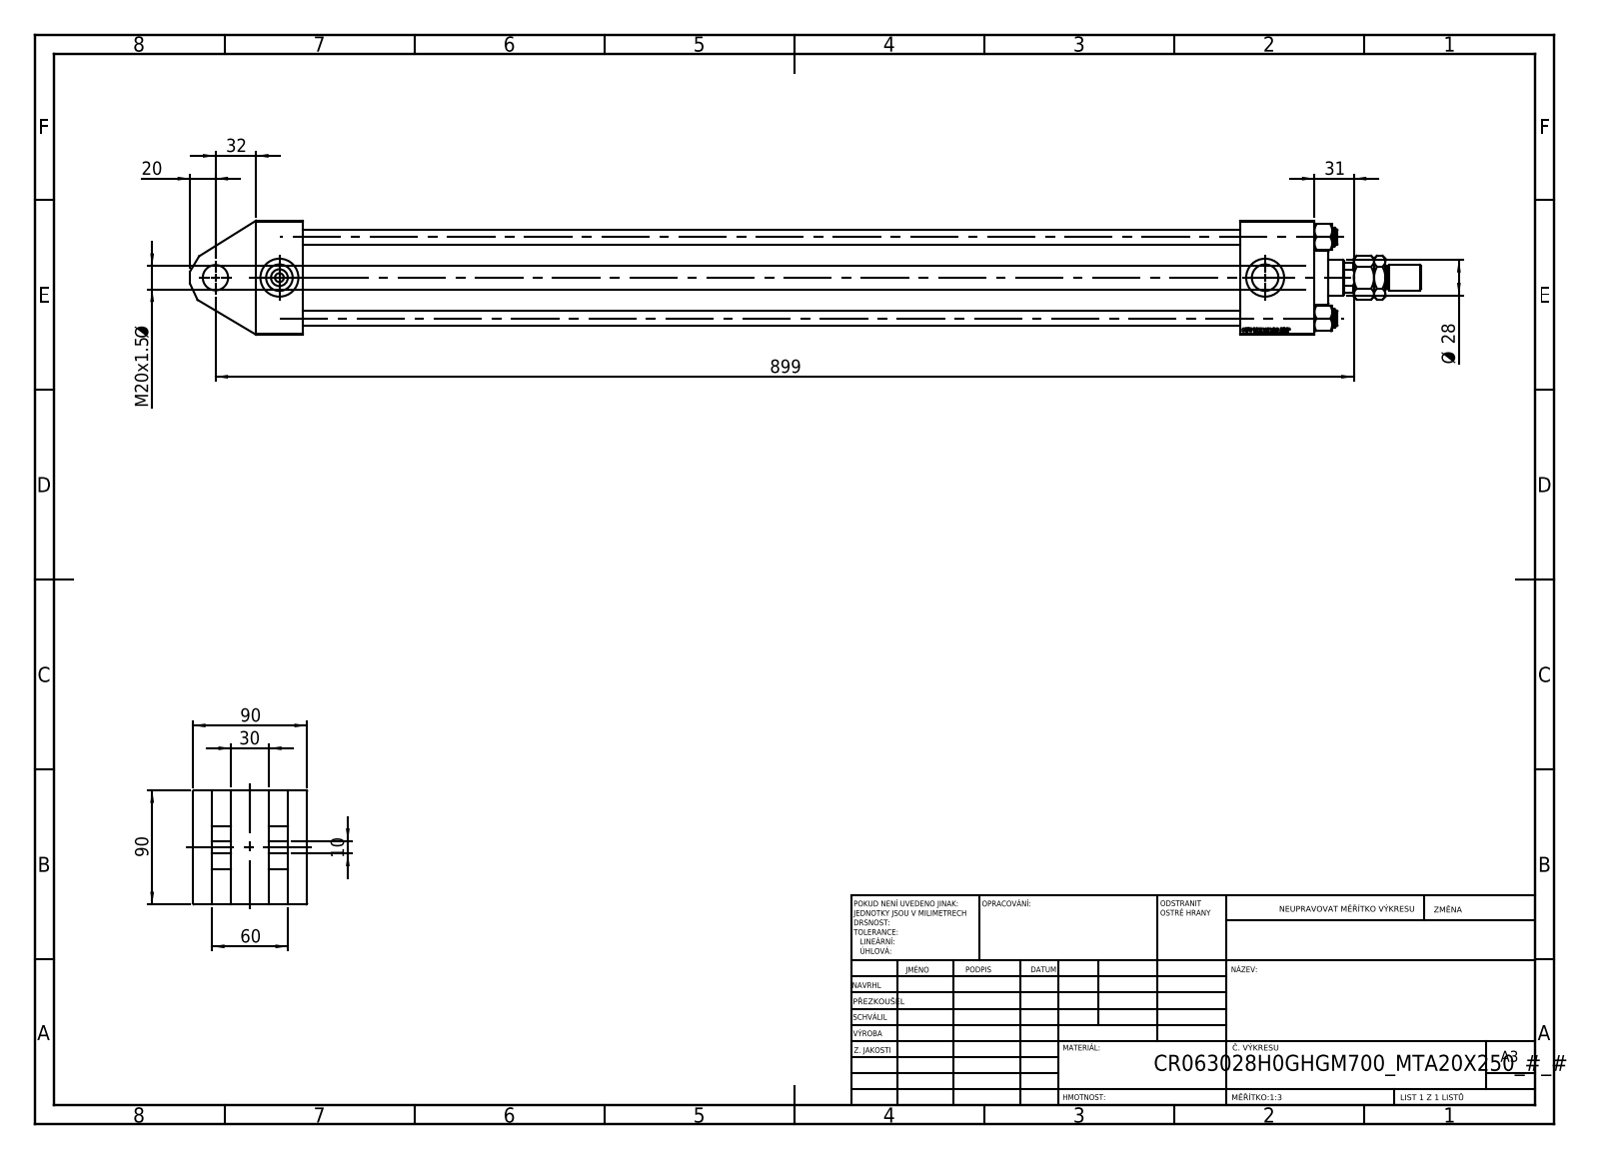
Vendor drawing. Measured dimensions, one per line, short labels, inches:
name: V215CR_TYCINKA_H; NUT_M5_H; V215CR_VCP_H; V215CR_H_Body (+2 more)
written by: SolidWorks 2019 (CONFIG_CONTROL_DESIGN)
unit: in
bodies: 12 solids, 1178 faces (533 planar, 87 cylindrical, 558 other)
size: 38.268 × 3.543 × 3.543
volume: 135.3 in³; area: 1 003 in²
holes: 4× ⌀0.472, 2× ⌀0.276, 2× ⌀0.825, 2× ⌀1.181, 1× ⌀0.728, 1× ⌀0.787, 1× ⌀1.102, 1× ⌀1.22, 1× ⌀1.969, 1× ⌀2.362, 1× ⌀2.48
bosses: 4× ⌀0.591, 1× ⌀2.717, 1× ⌀1.654, 1× ⌀0.787, 1× ⌀0.709
rounds: 1× R0.531
face distances: 3.543, 0.591, 1.181, 2.362, 31.457, 1.772, 2.953, 1.457, 32.913, 30.591
hole spacings: 1.79, 2.531, 3.58, 1.988, 30.65, 32.638
